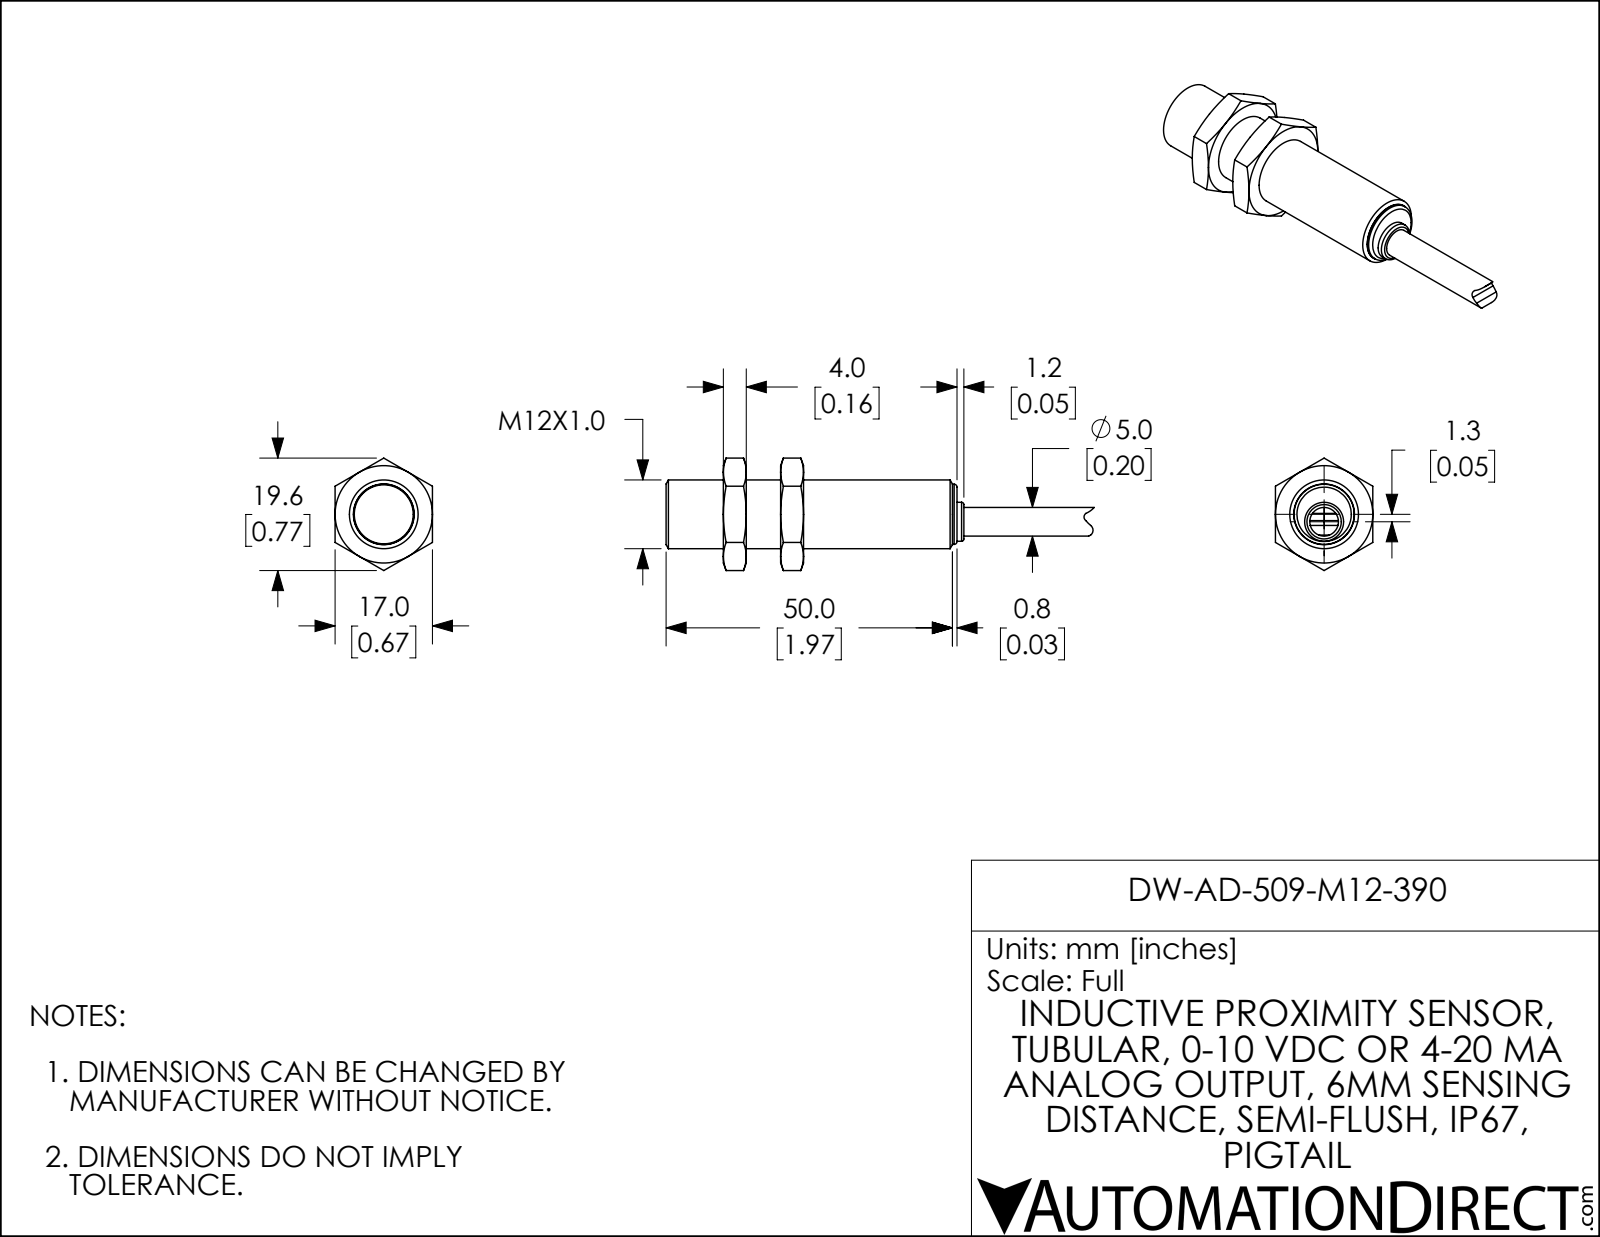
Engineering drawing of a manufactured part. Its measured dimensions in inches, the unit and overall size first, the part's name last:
Units: inches
Overall size (bounding box): 2.943 × 0.773 × 0.669
Round holes (diameter × count): ⌀0.415 ×1
Round bosses / shafts (diameter × count): ⌀0.472 ×1, ⌀0.413 ×1, ⌀0.406 ×1, ⌀0.268 ×1, ⌀0.197 ×1
Partial cylindrical surfaces — rounded edges, fillets, slot ends (radius × count): R0.031 ×1, R0.041 ×1, R0.165 ×1, R0.248 ×1, R0.331 ×1
Main face-to-face distances: 0.394, 0.157, 0.669, 0.551, 0.236, 0.787, 0.945, 2, 1.606, 1.449
Volume: 0.443 in³ · Surface area: 4.915 in²
Bodies: 1 solid, 63 faces (22 planar, 13 cylindrical, 28 other)
Part name (STEP PRODUCT): DW-AD-509-M12-390
STEP written by: PARTsolutions (CONFIG_CONTROL_DESIGN)
